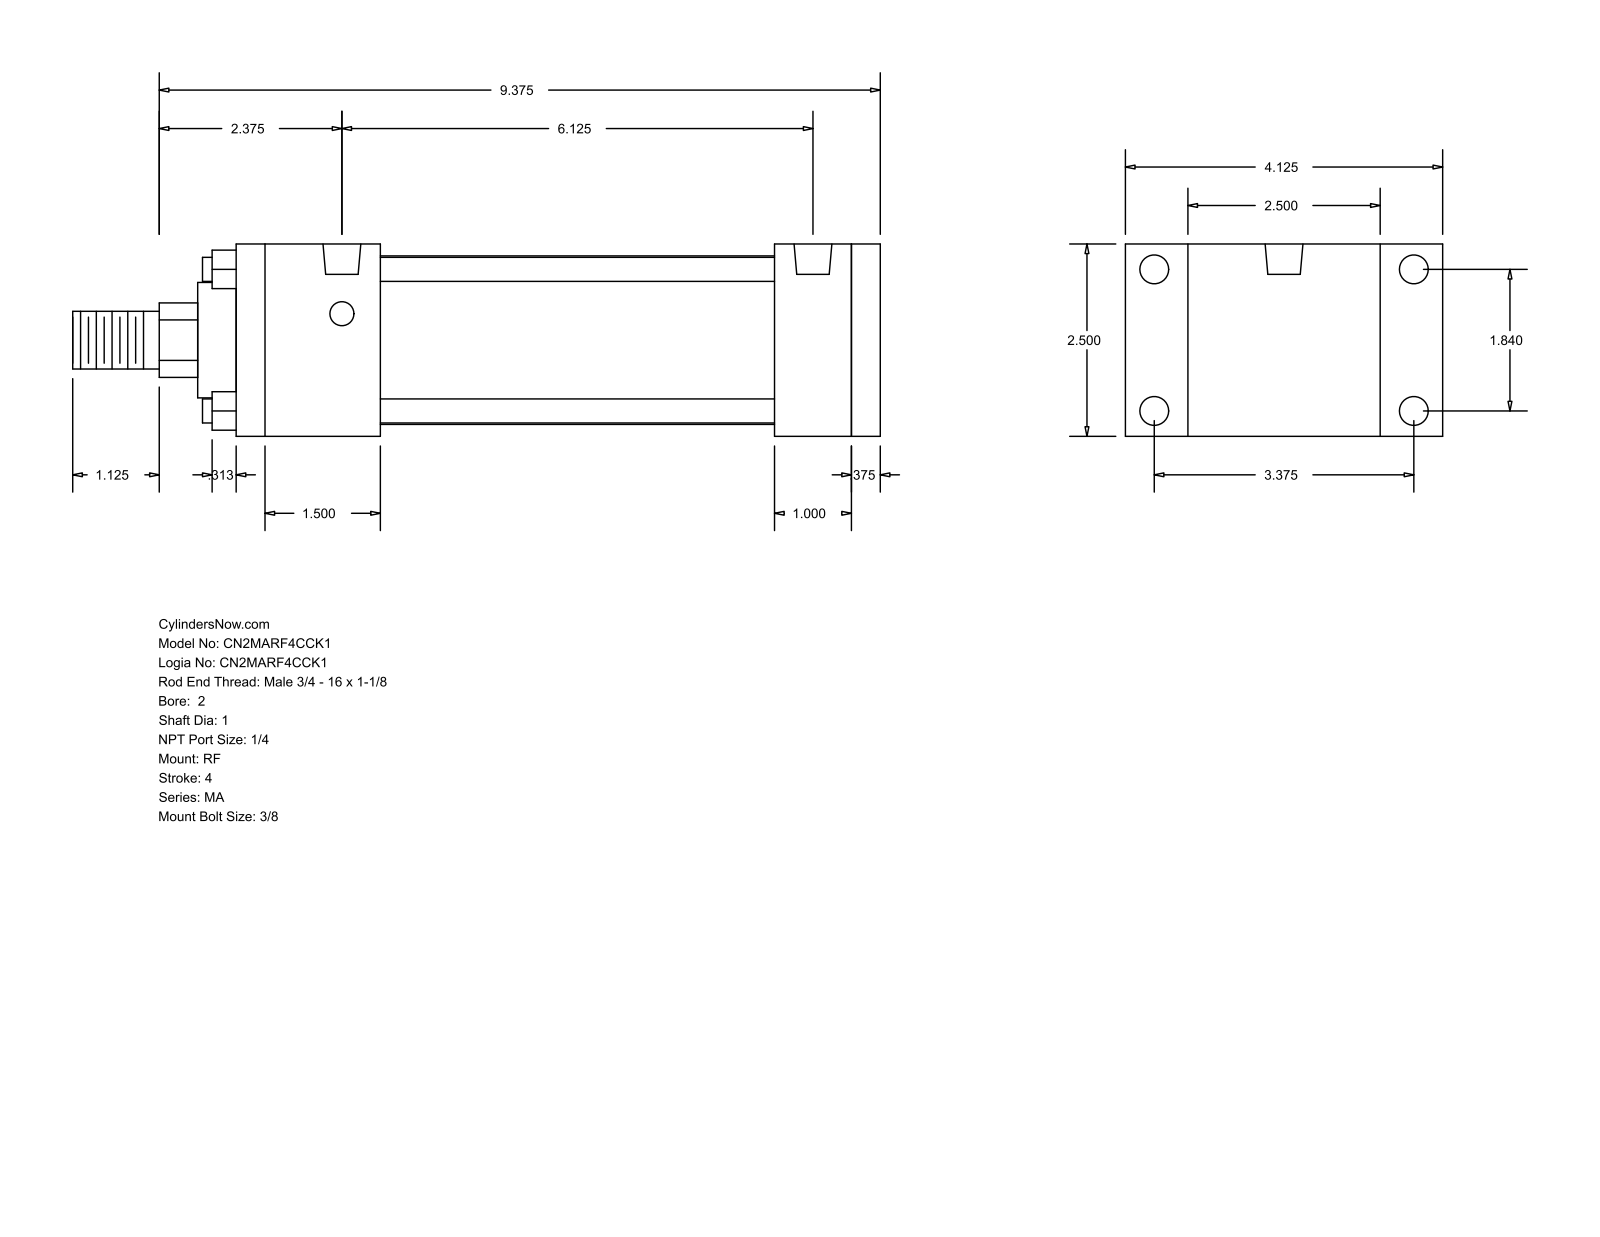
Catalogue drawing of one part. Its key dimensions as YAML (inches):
part_name: "MA_RF__0200_1"
step_written_by: "GSSL Pune (CONFIG_CONTROL_DESIGN)"
units: inches
bodies: {solids: 0, faces: 92, planar: 64, cylindrical: 28, other: 0}
overall_size: [10.5, 4.125, 2.5]
round_holes:
  - {diameter: 0.313, count: 4}
  - {diameter: 0.375, count: 4}
  - {diameter: 0.492, count: 2}
round_bosses_or_shafts:
  - {diameter: 0.313, count: 4}
  - {diameter: 2.19, count: 1}
  - {diameter: 1.5, count: 1}
  - {diameter: 1, count: 1}
  - {diameter: 0.75, count: 1}
partial_cylinders:
  - {radius: 0.484, count: 1}
face_to_face_distances: [2.5, 8, 0.375, 8.375, 1, 0.813, 0.5, 1.875, 6.125, 6.5]
hole_center_spacings: [1.84, 3.375, 3.844, 6.125]
